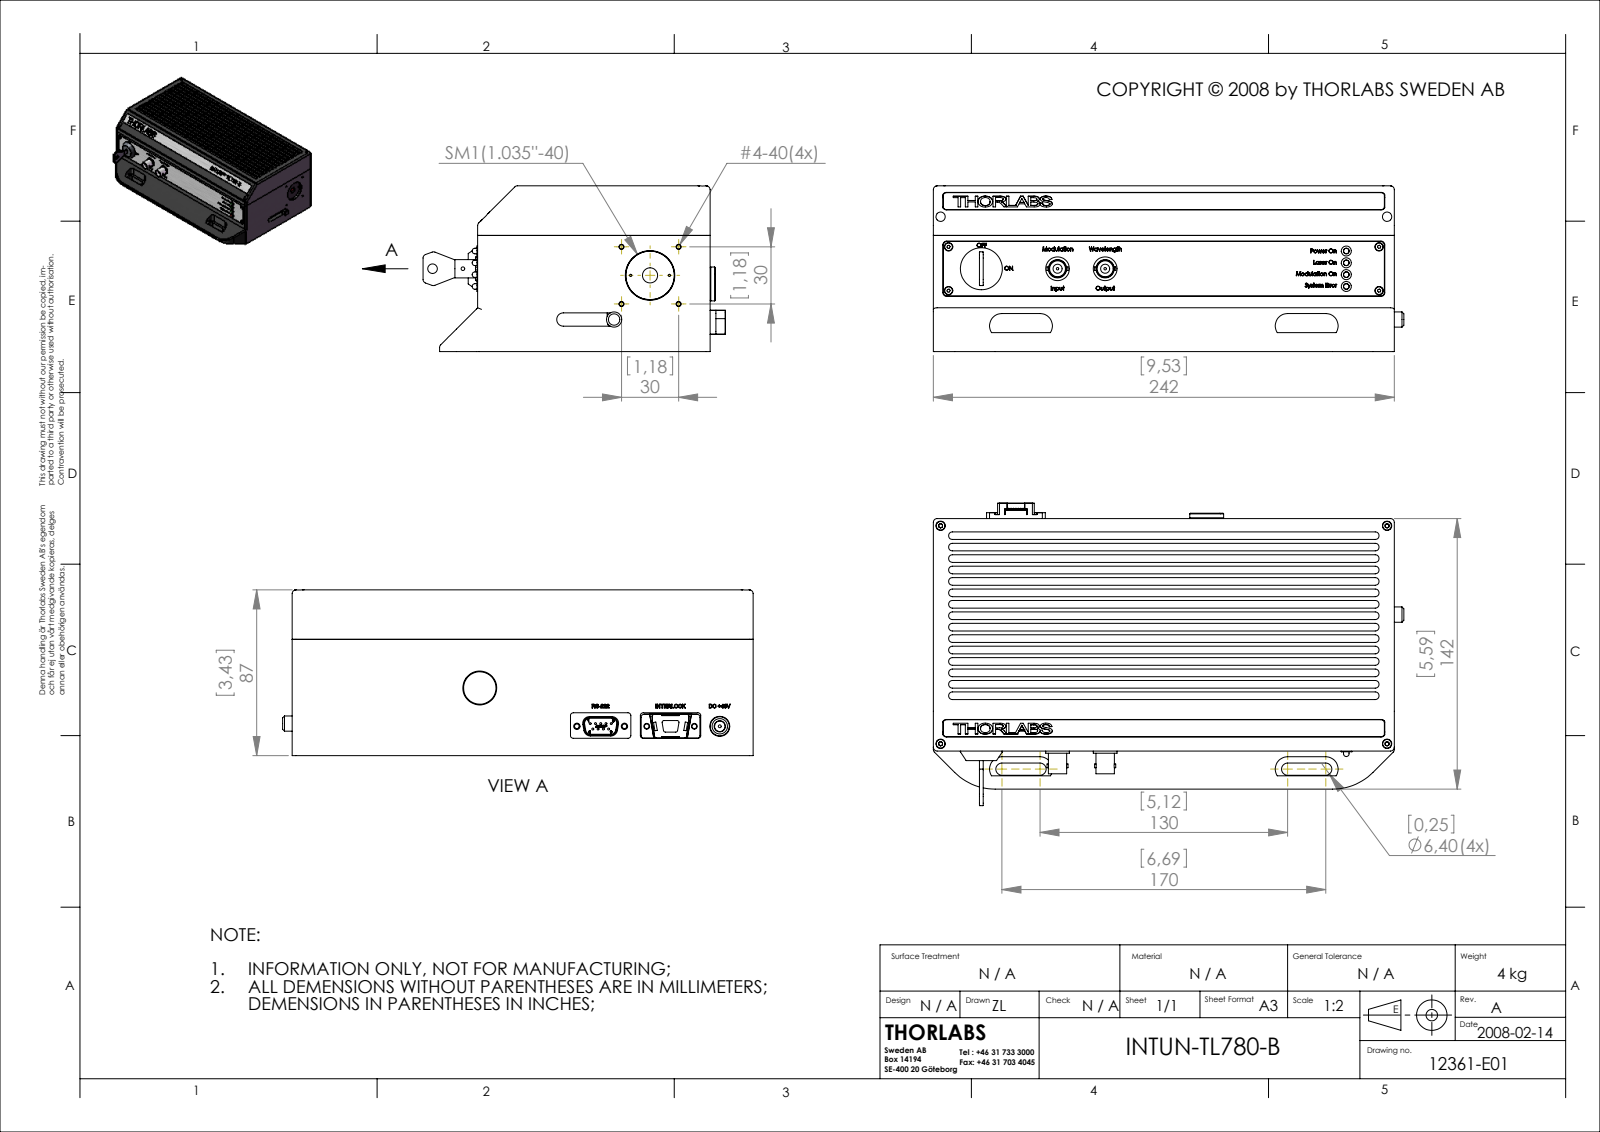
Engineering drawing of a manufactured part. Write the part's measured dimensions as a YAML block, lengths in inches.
part_name: "INTUN-TL780-B"
step_written_by: "SolidWorks 2007 (CONFIG_CONTROL_DESIGN)"
units: inches
bodies: {solids: 0, faces: 3221, planar: 1789, cylindrical: 628, other: 804}
overall_size: [9.744, 6.247, 3.425]
round_holes:
  - {diameter: 0.04, count: 9}
  - {diameter: 0.081, count: 8}
  - {diameter: 0.063, count: 4}
  - {diameter: 0.089, count: 4}
  - {diameter: 0.094, count: 4}
  - {diameter: 0.098, count: 4}
  - {diameter: 0.114, count: 4}
  - {diameter: 0.118, count: 4}
  - {diameter: 0.12, count: 4}
  - {diameter: 0.169, count: 4}
  - {diameter: 0.177, count: 4}
  - {diameter: 0.193, count: 4}
round_bosses_or_shafts:
  - {diameter: 0.04, count: 9}
  - {diameter: 0.177, count: 5}
  - {diameter: 0.098, count: 5}
  - {diameter: 0.244, count: 4}
  - {diameter: 0.209, count: 4}
  - {diameter: 0.185, count: 4}
  - {diameter: 0.167, count: 4}
  - {diameter: 0.157, count: 4}
partial_cylinders:
  - {radius: 0.079, count: 68}
  - {radius: 0.062, count: 16}
  - {radius: 0.008, count: 14}
  - {radius: 0.197, count: 14}
  - {radius: 0.138, count: 10}
  - {radius: 0.236, count: 10}
  - {radius: 0.028, count: 9}
  - {radius: 0.037, count: 9}
face_to_face_distances: [0.236, 0.22, 0.246, 3.061, 2.841, 4.567, 0.079, 0.039, 3.268, 0.207]
hole_center_spacings: [0.109, 0.906, 0.835, 1.181, 0.124, 0.198, 0.218, 0.244]
